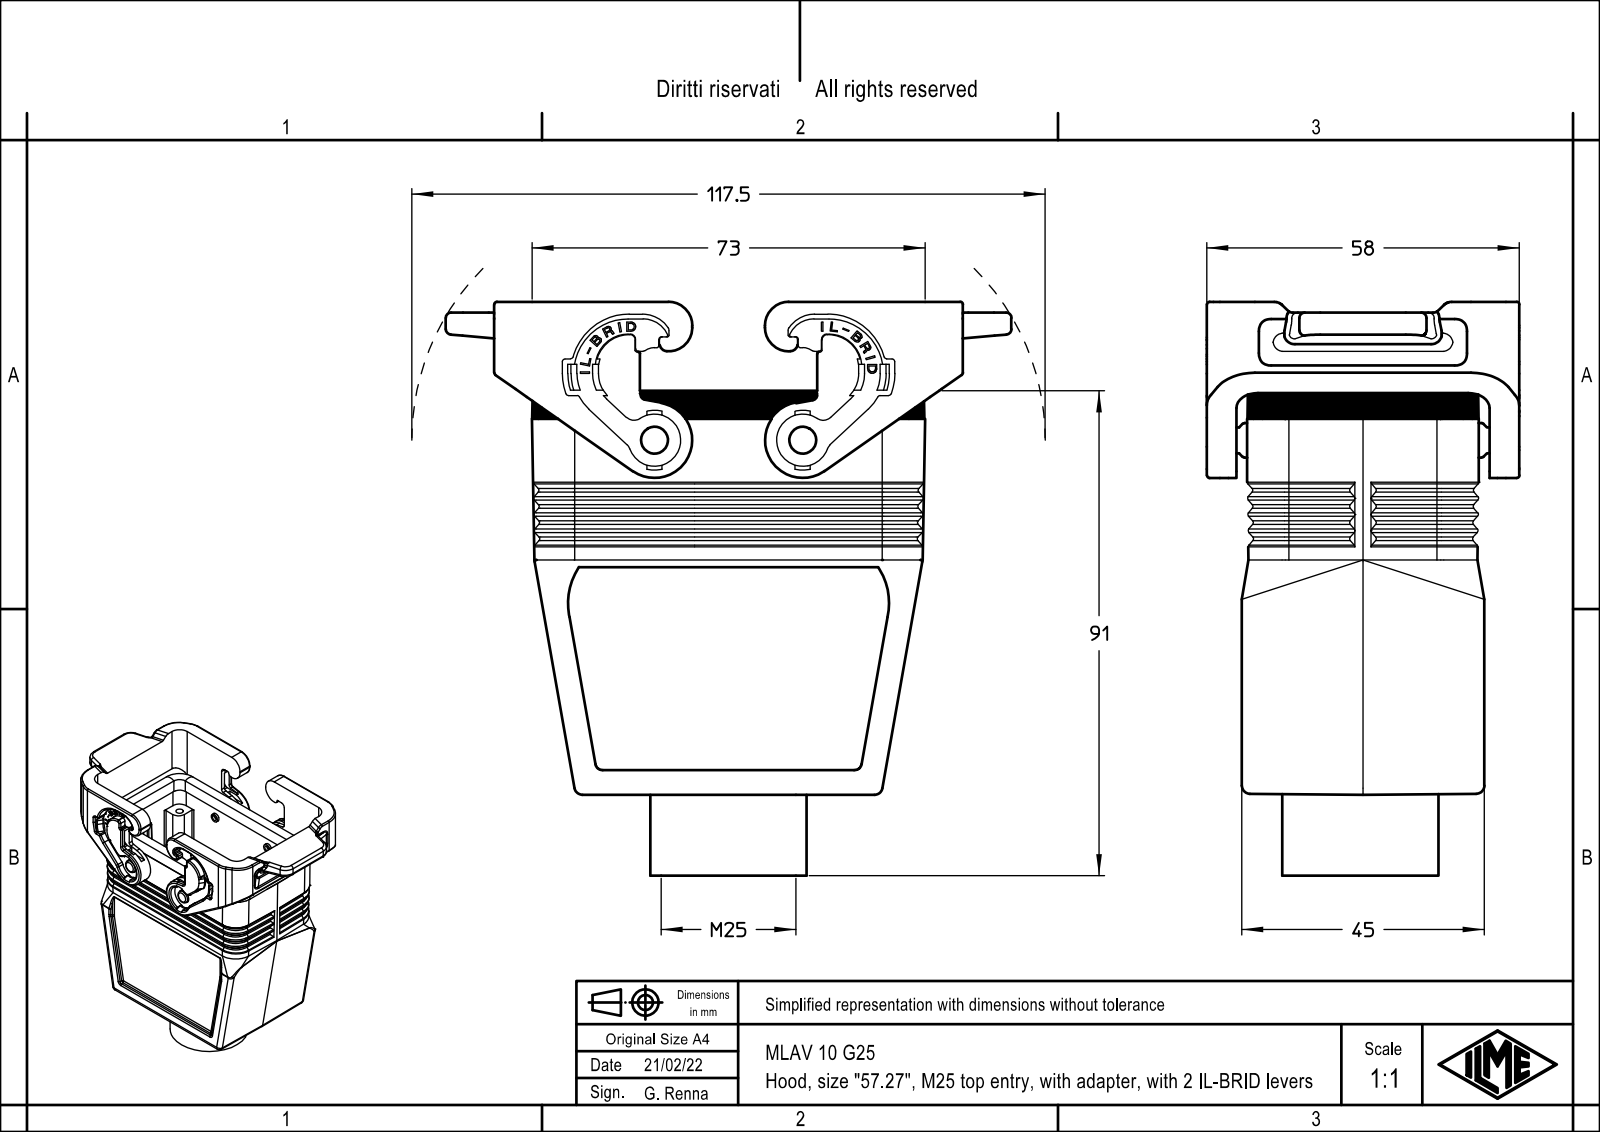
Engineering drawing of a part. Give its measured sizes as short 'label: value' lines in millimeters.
name: MLAV_10_G25
written by: Creo Elements/Direct Modeling 20.1B 02-Apr-2019 (C) Parametric Technology GmbH (AUTOMOTIVE_DESIGN)
unit: mm
bodies: 1 solid, 1487 faces (960 planar, 335 cylindrical, 192 other)
size: 106.45 × 105 × 58
volume: 100 883 mm³; area: 52 550 mm²
holes: 4× ⌀2.75, 1× ⌀20, 1× ⌀25
bosses: 2× ⌀6.8, 2× ⌀4.8, 1× ⌀29
rounds: 54× R1, 43× R0.5, 20× R3, 16× R7, 15× R0.33, 14× R1.5, 8× R0.3, 8× R2
face distances: 39.25, 2, 3.75, 5.75, 1, 45, 41.25, 43, 4.75, 40.25
hole spacings: 31.54, 27, 57, 63.07
